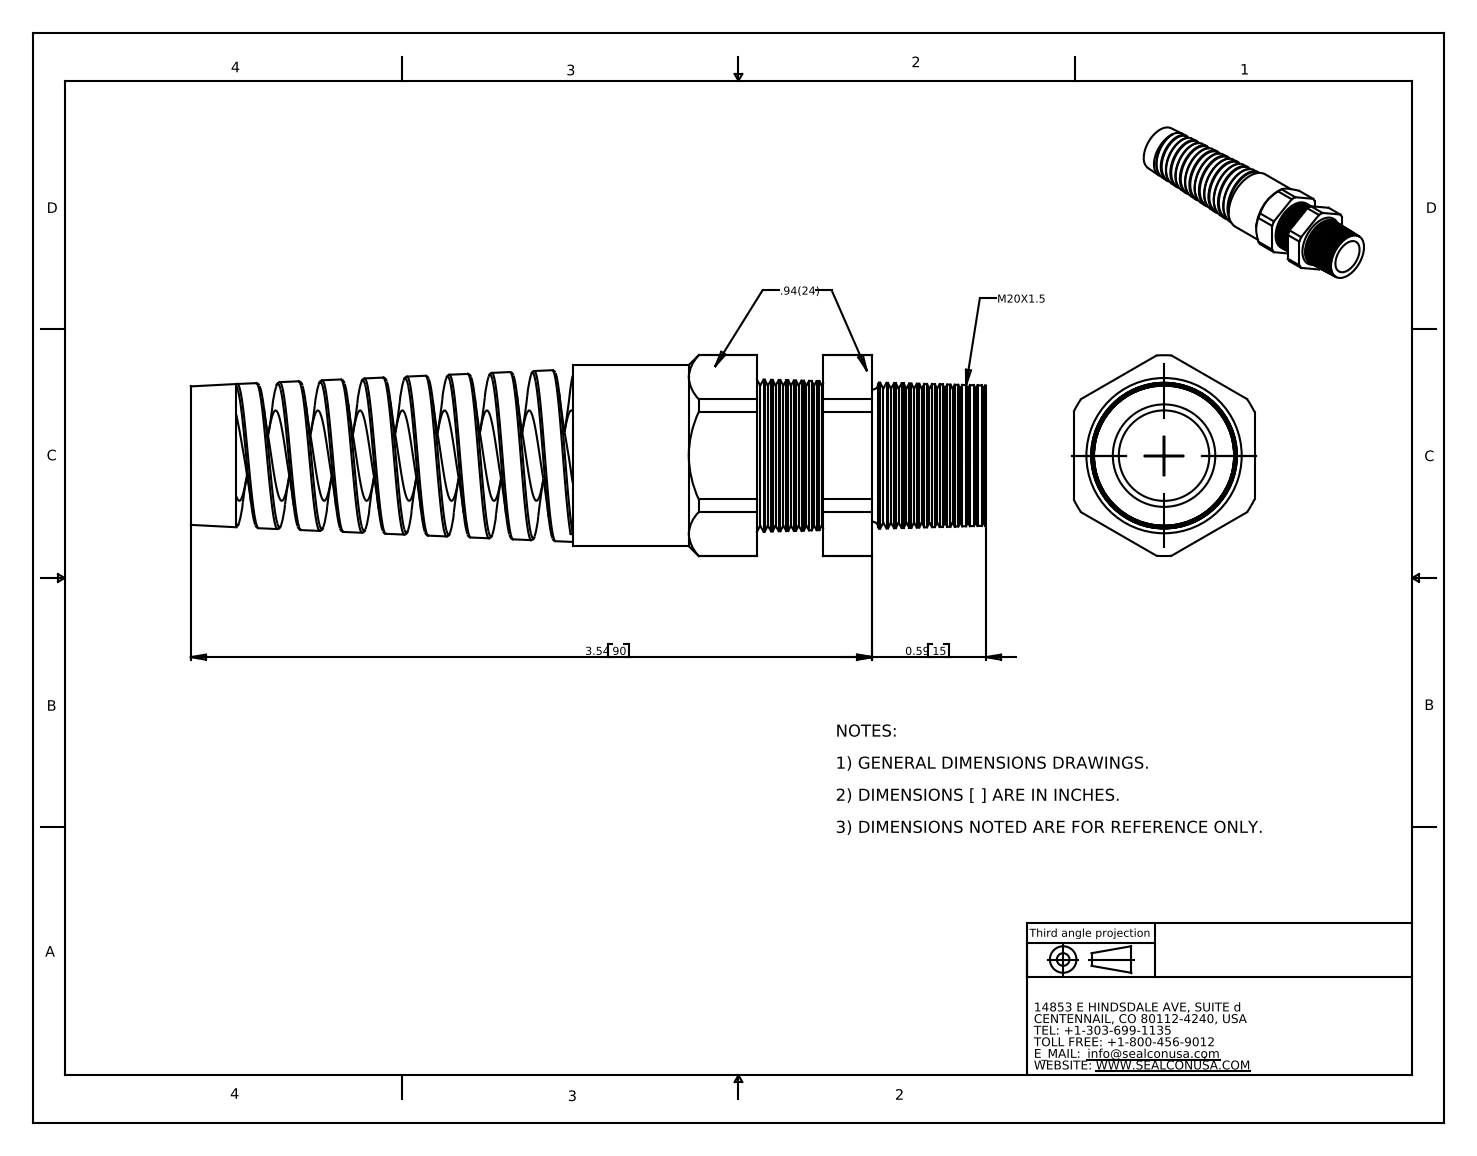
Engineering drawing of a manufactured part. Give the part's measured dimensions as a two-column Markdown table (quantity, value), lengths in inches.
| quantity | value |
| --- | --- |
| part name | CF20DA-BK |
| STEP written by | SolidWorks 2007 (CONFIG_CONTROL_DESIGN) |
| units | inches |
| bodies | 2 solids, 248 faces (25 planar, 41 cylindrical, 182 other) |
| overall size | 4.13 × 1.043 × 0.94 |
| volume | 1.312 in³ |
| surface area | 23.79 in² |
| round holes (diameter × count) | 0.47 × 1, 0.495 × 1 |
| round bosses / shafts (diameter × count) | 0.94 × 1, 0.686 × 1 |
| partial cylindrical surfaces (radius × count) | 0.522 × 1 |
| main face-to-face distances | 0.94, 0.344, 0.6, 0.256, 0.957, 1.301, 1.557, 0.603, 0.354, 0.698 |
